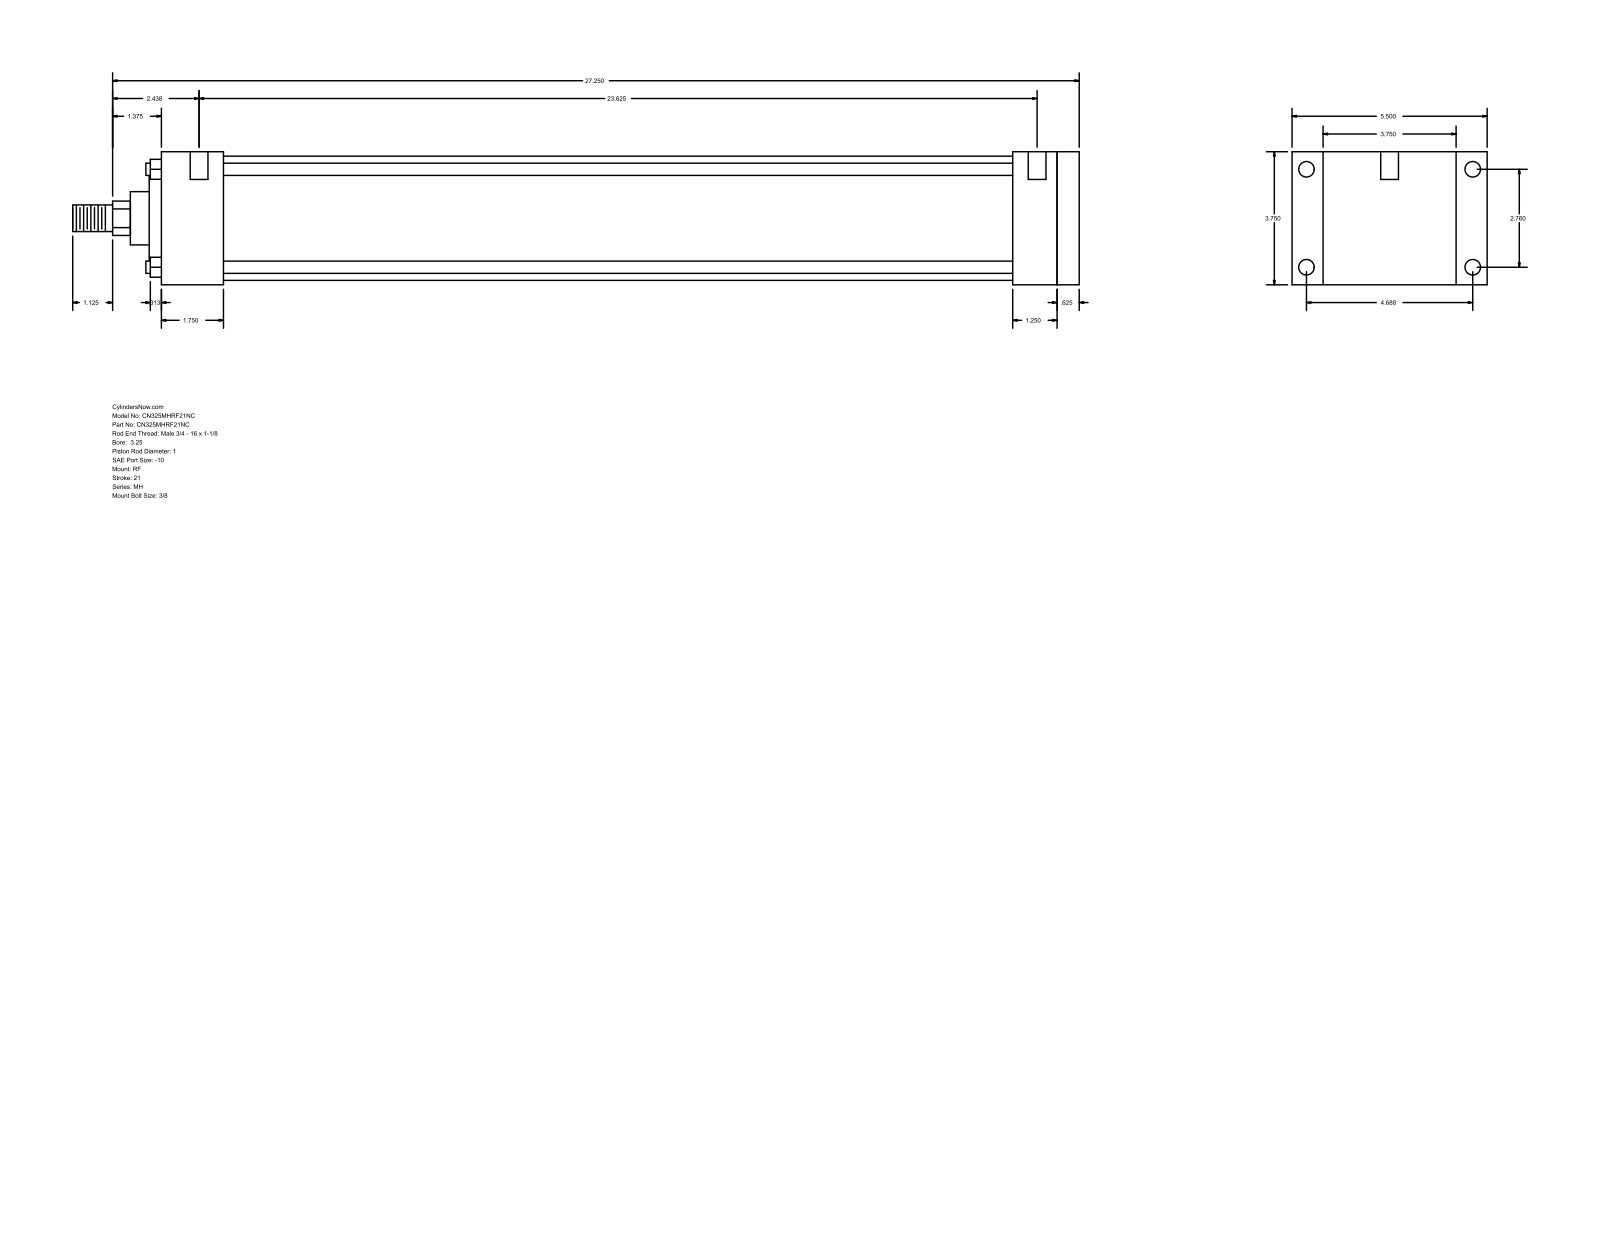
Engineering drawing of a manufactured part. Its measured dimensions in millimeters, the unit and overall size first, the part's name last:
Units: millimetres
Overall size (bounding box): 720.73 × 139.7 × 95.25
Round holes (diameter × count): ⌀5.56 ×4, ⌀11.13 ×4, ⌀12.7 ×2
Round bosses / shafts (diameter × count): ⌀8.76 ×4, ⌀88.9 ×1, ⌀60.33 ×1, ⌀38.1 ×1, ⌀25.4 ×1, ⌀19.05 ×1
Partial cylindrical surfaces — rounded edges, fillets, slot ends (radius × count): R12.29 ×1
Main face-to-face distances: 95.24, 657.23, 641.35, 15.88, 22.23, 117.47, 44.46, 596.89, 612.77, 609.6
Hole centre spacings: 70.1, 119.06, 138.16, 606.42, 1.58, 4.76, 600.08, 601.66
Bodies: 0 solids, 94 faces (65 planar, 29 cylindrical, 0 other)
Part name (STEP PRODUCT): MH_RF__0325_1
STEP written by: GSSL Pune (CONFIG_CONTROL_DESIGN)
